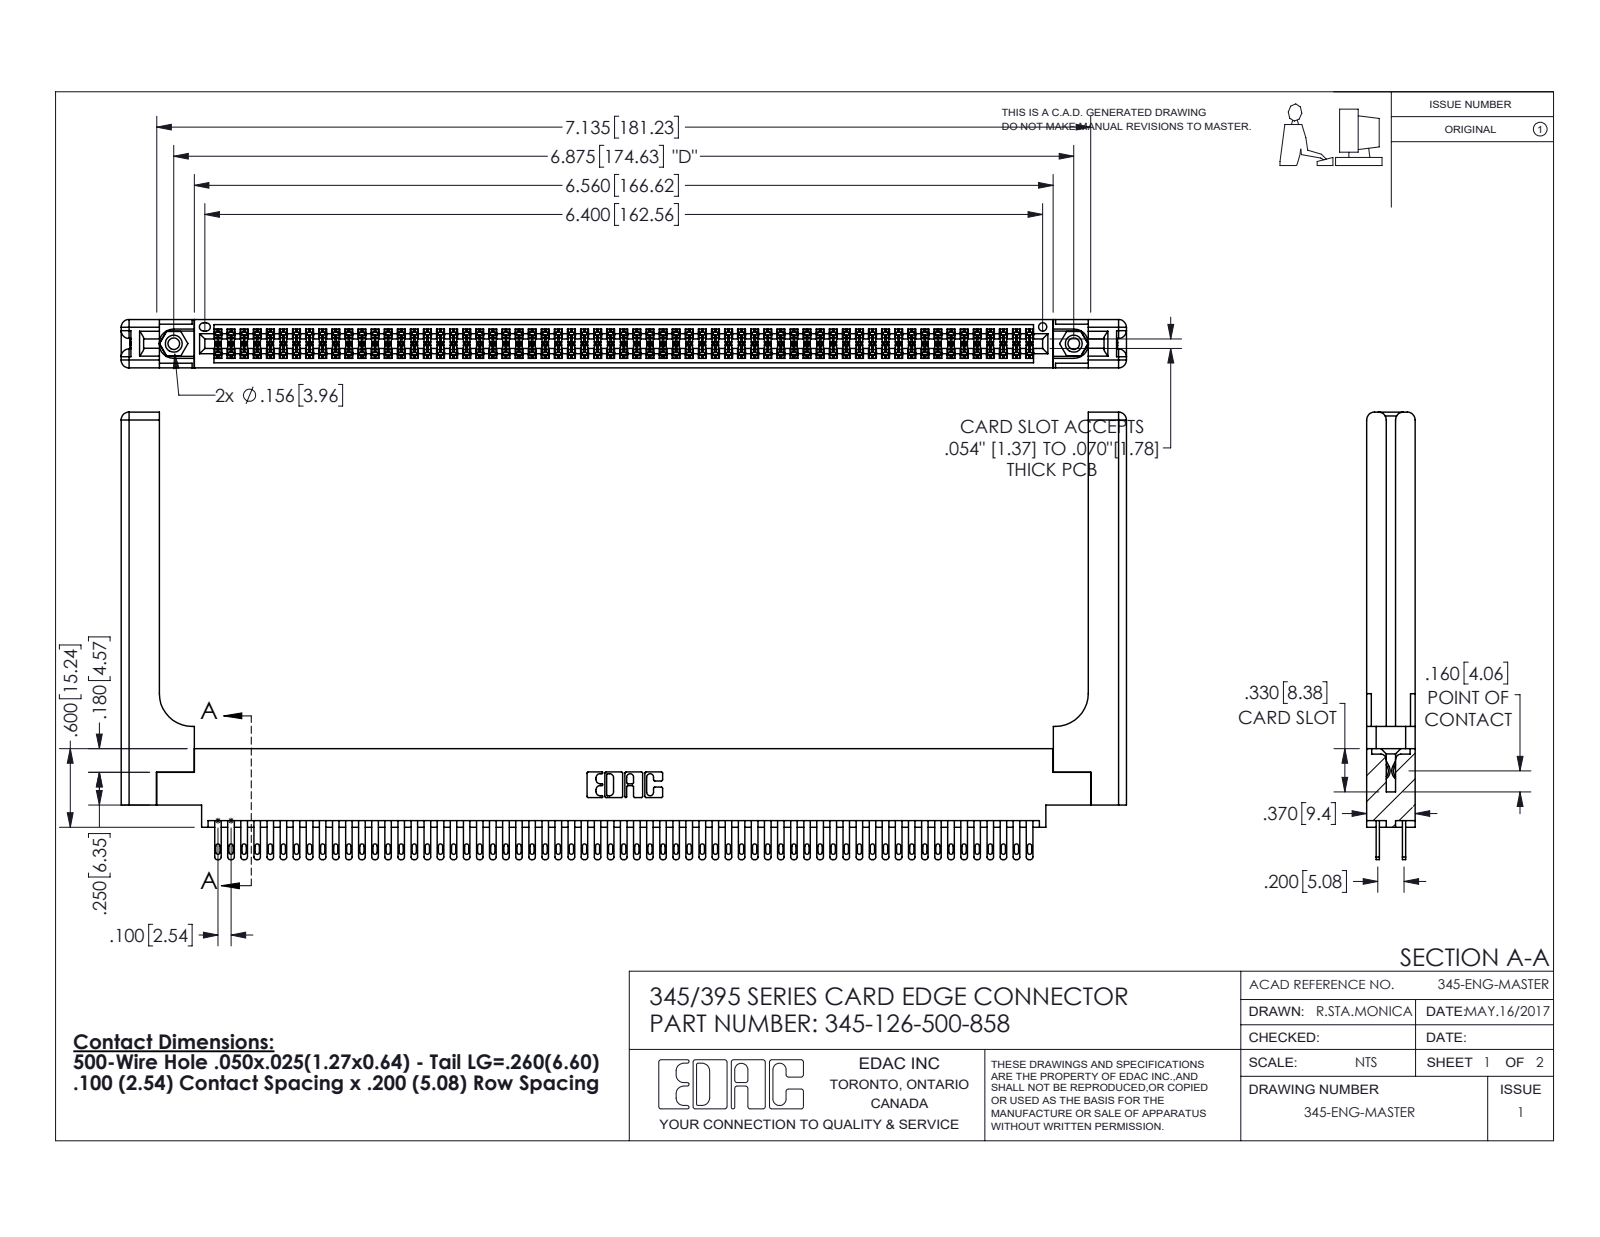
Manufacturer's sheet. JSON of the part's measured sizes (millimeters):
{"part_name": "345 Part_0.170 Offset - 0.156 Dia-TH; 345-220-058_345-220-058; 345-126-500-858; 345-250-001_345-250-001-102 (+1 more)", "step_written_by": "SolidWorks 2016 (CONFIG_CONTROL_DESIGN)", "units": "millimeters", "bodies": {"solids": 131, "faces": 6182, "planar": 3634, "cylindrical": 2488, "other": 60}, "overall_size": [195, 86.8, 9.4], "volume_mm3": 27890, "surface_area_mm2": 35590, "round_holes": [[2.3, 2], [3.2, 2], [4, 2], [1.6, 1]], "round_bosses_or_shafts": [[3.9, 2]], "partial_cylinders_radius": [[0.2, 189], [0.4, 126], [0.5, 126], [0.3, 22], [1.5, 16], [0.2, 6], [0.8, 6], [0.7, 3]], "face_to_face_distances": [1.8, 7.6, 9.4, 2.5, 6.9, 0.6, 5.1, 5.7, 4.4, 3.8], "hole_center_spacings": [6.9, 168.6, 174.6]}
